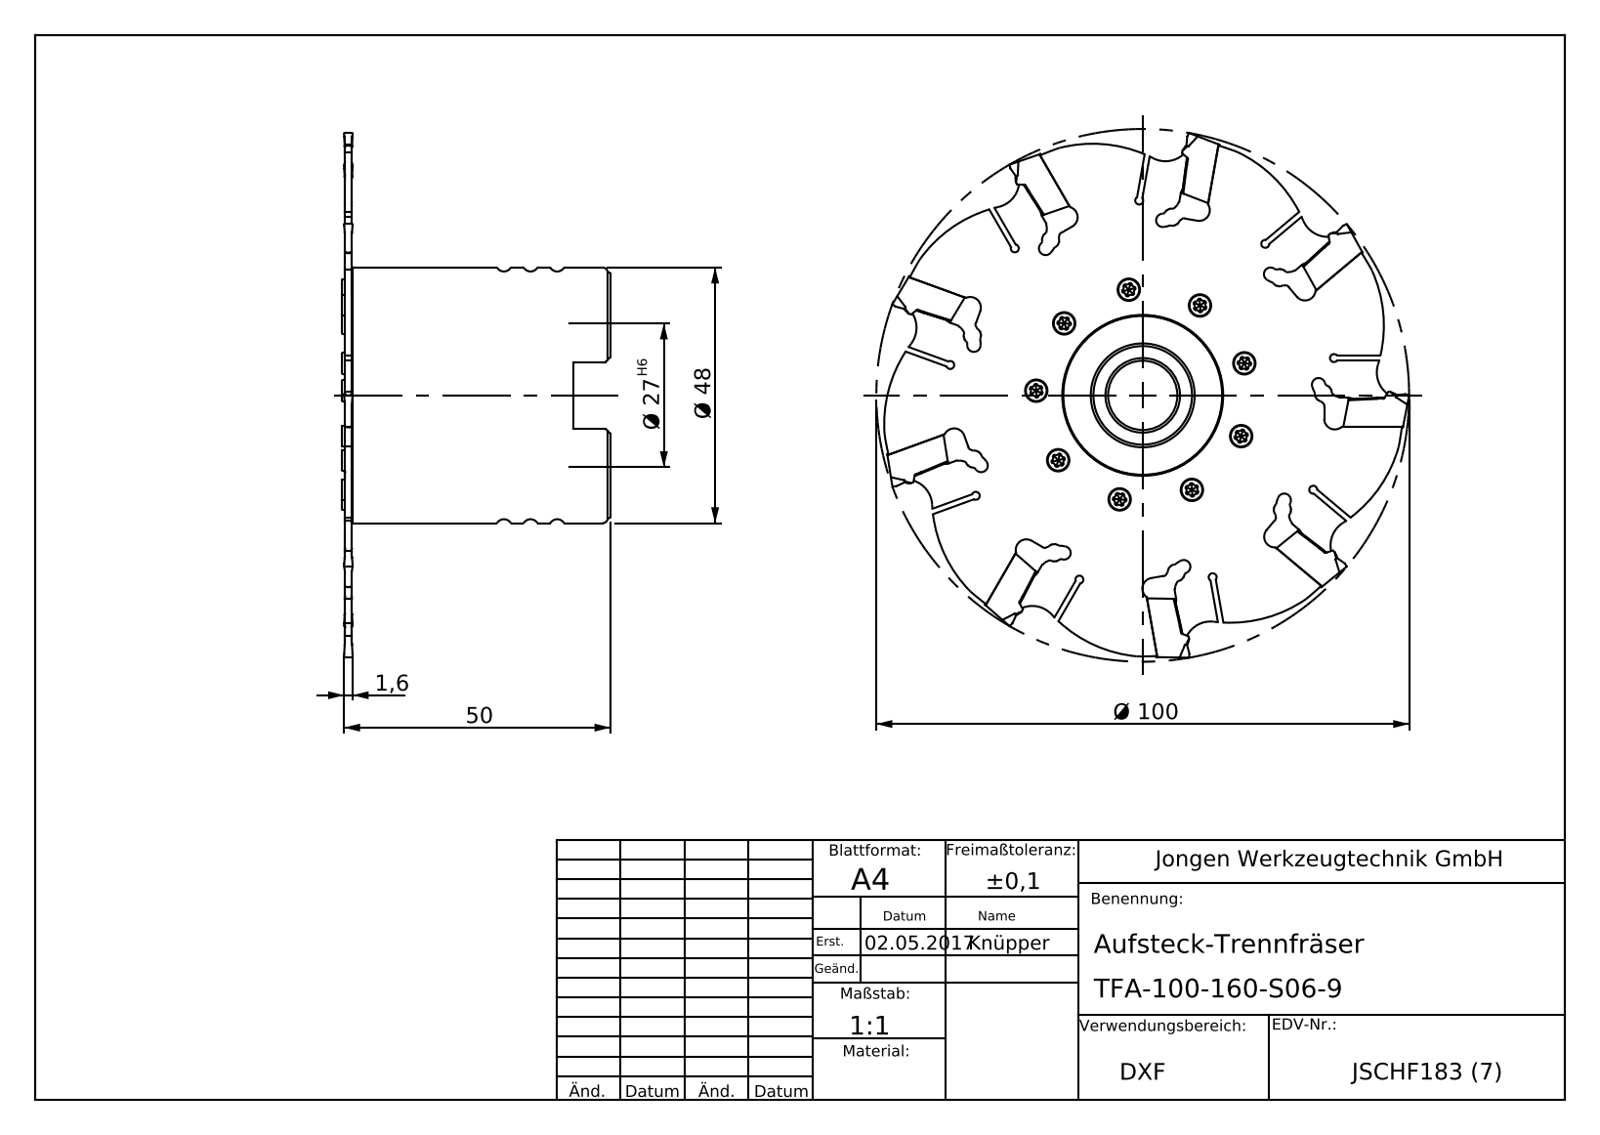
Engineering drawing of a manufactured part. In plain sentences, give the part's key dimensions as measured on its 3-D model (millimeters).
The part is named "JSCHF183 pk; JSCHF183_1 pk; TFA-100-160-S06-9". Its 3-D file was written by "SolidWorks 2018 (AUTOMOTIVE_DESIGN)". It is 2 solids with 170 faces: 20 planar, 64 cylindrical and 86 other. Overall it measures 100 by 100 by 50 millimeters. Its volume is 76 510 cubic millimeters and its surface area 29 645 square millimeters. Round holes: 9 of diameter 2.5, 9 of diameter 3.2, 1 of diameter 13, 1 of diameter 18.5, 1 of diameter 27, 1 of diameter 27.15, 1 of diameter 27.3, 1 of diameter 30, 1 of diameter 62.26. Round bosses or shafts: 1 of diameter 100, 1 of diameter 48. The main face-to-face distances are 1.4, 1.6, 1.2, 25, 48.4, 48.6, 49.8, 50, 23.4, 23.6. The hole center spacings are 20, 25.71, 13.68, 34.64, 39.39, 39.4, 34.65, 13.69.
